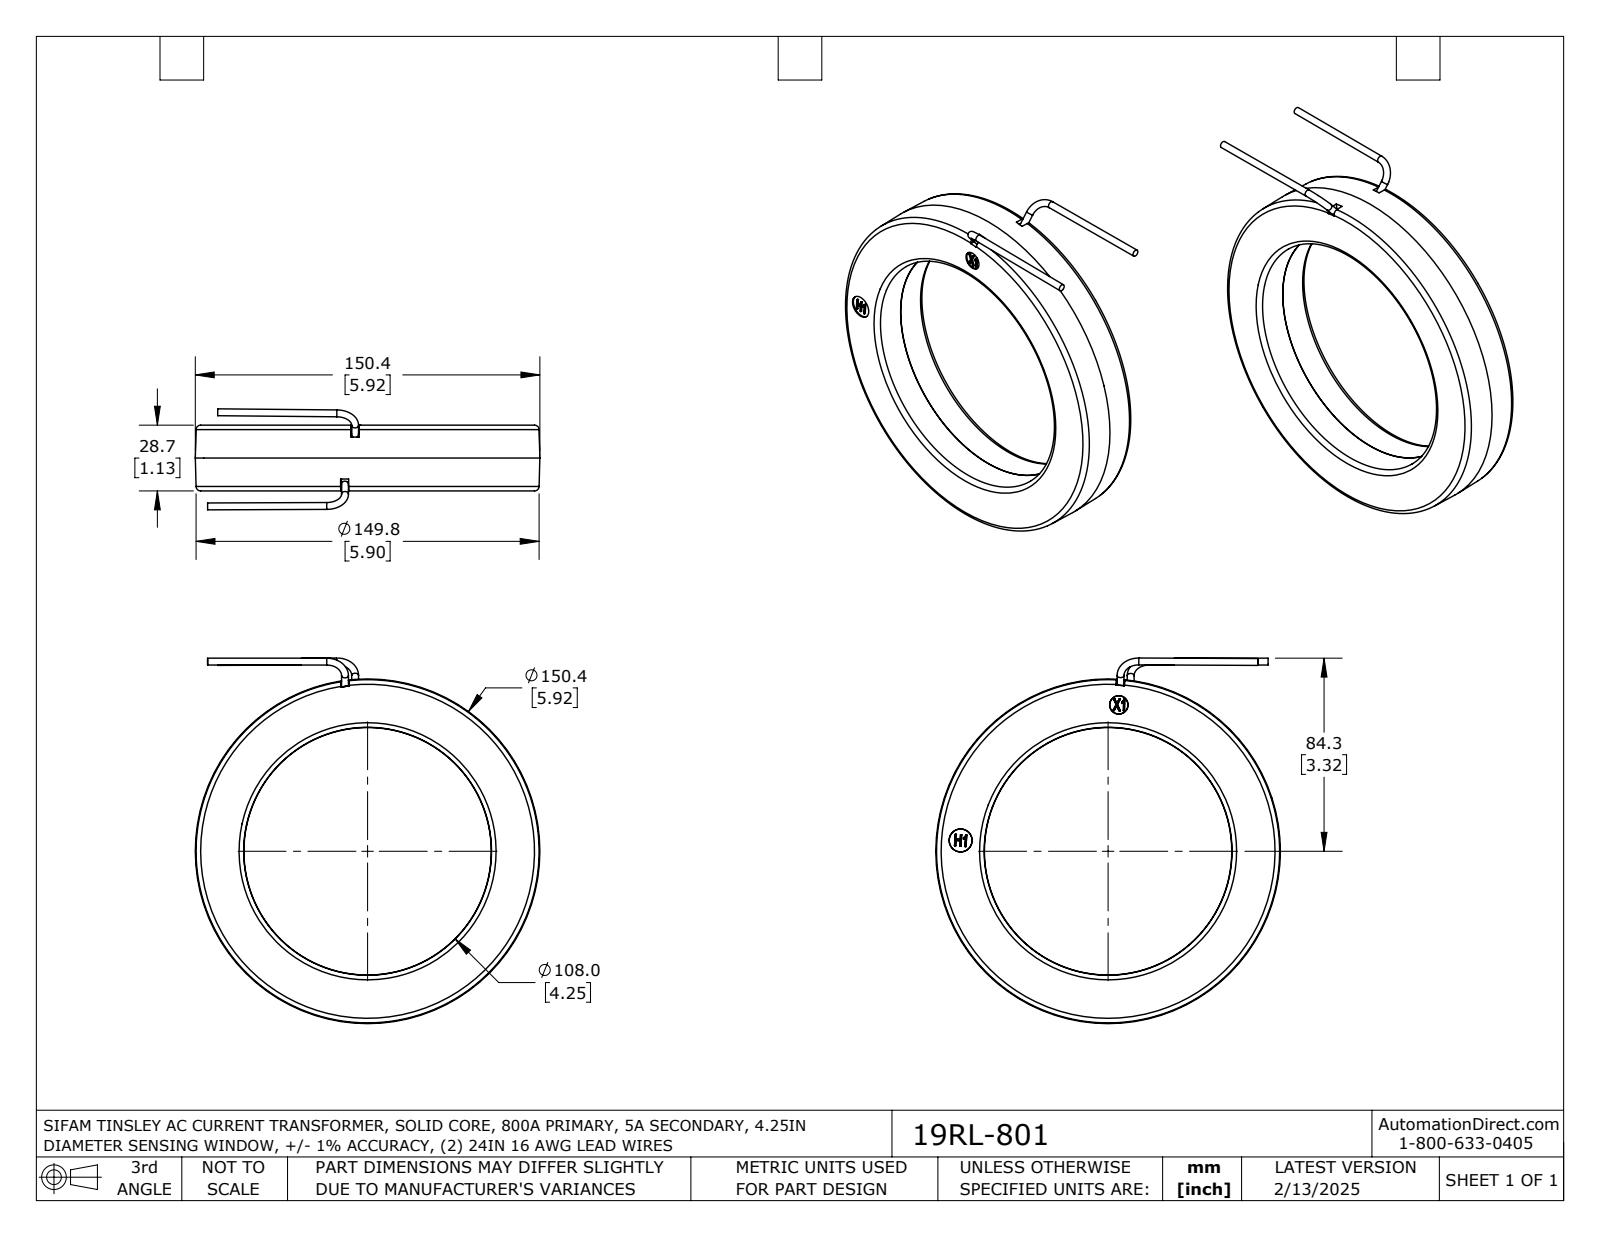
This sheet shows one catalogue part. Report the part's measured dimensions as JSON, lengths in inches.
{"part_name": "19RL-801", "step_written_by": "SolidWorks 2021 (AUTOMOTIVE_DESIGN)", "units": "inches", "bodies": {"solids": 1, "faces": 104, "planar": 52, "cylindrical": 8, "other": 44}, "overall_size": [6.282, 5.922, 1.734], "volume_in3": 14.81, "surface_area_in2": 85.38, "round_bosses_or_shafts": [[0.118, 4]], "face_to_face_distances": [0.563, 0.567, 1.13, 1.111, 0.548, 0.544, 0.019, 1.109, 0.546, 0.542]}
